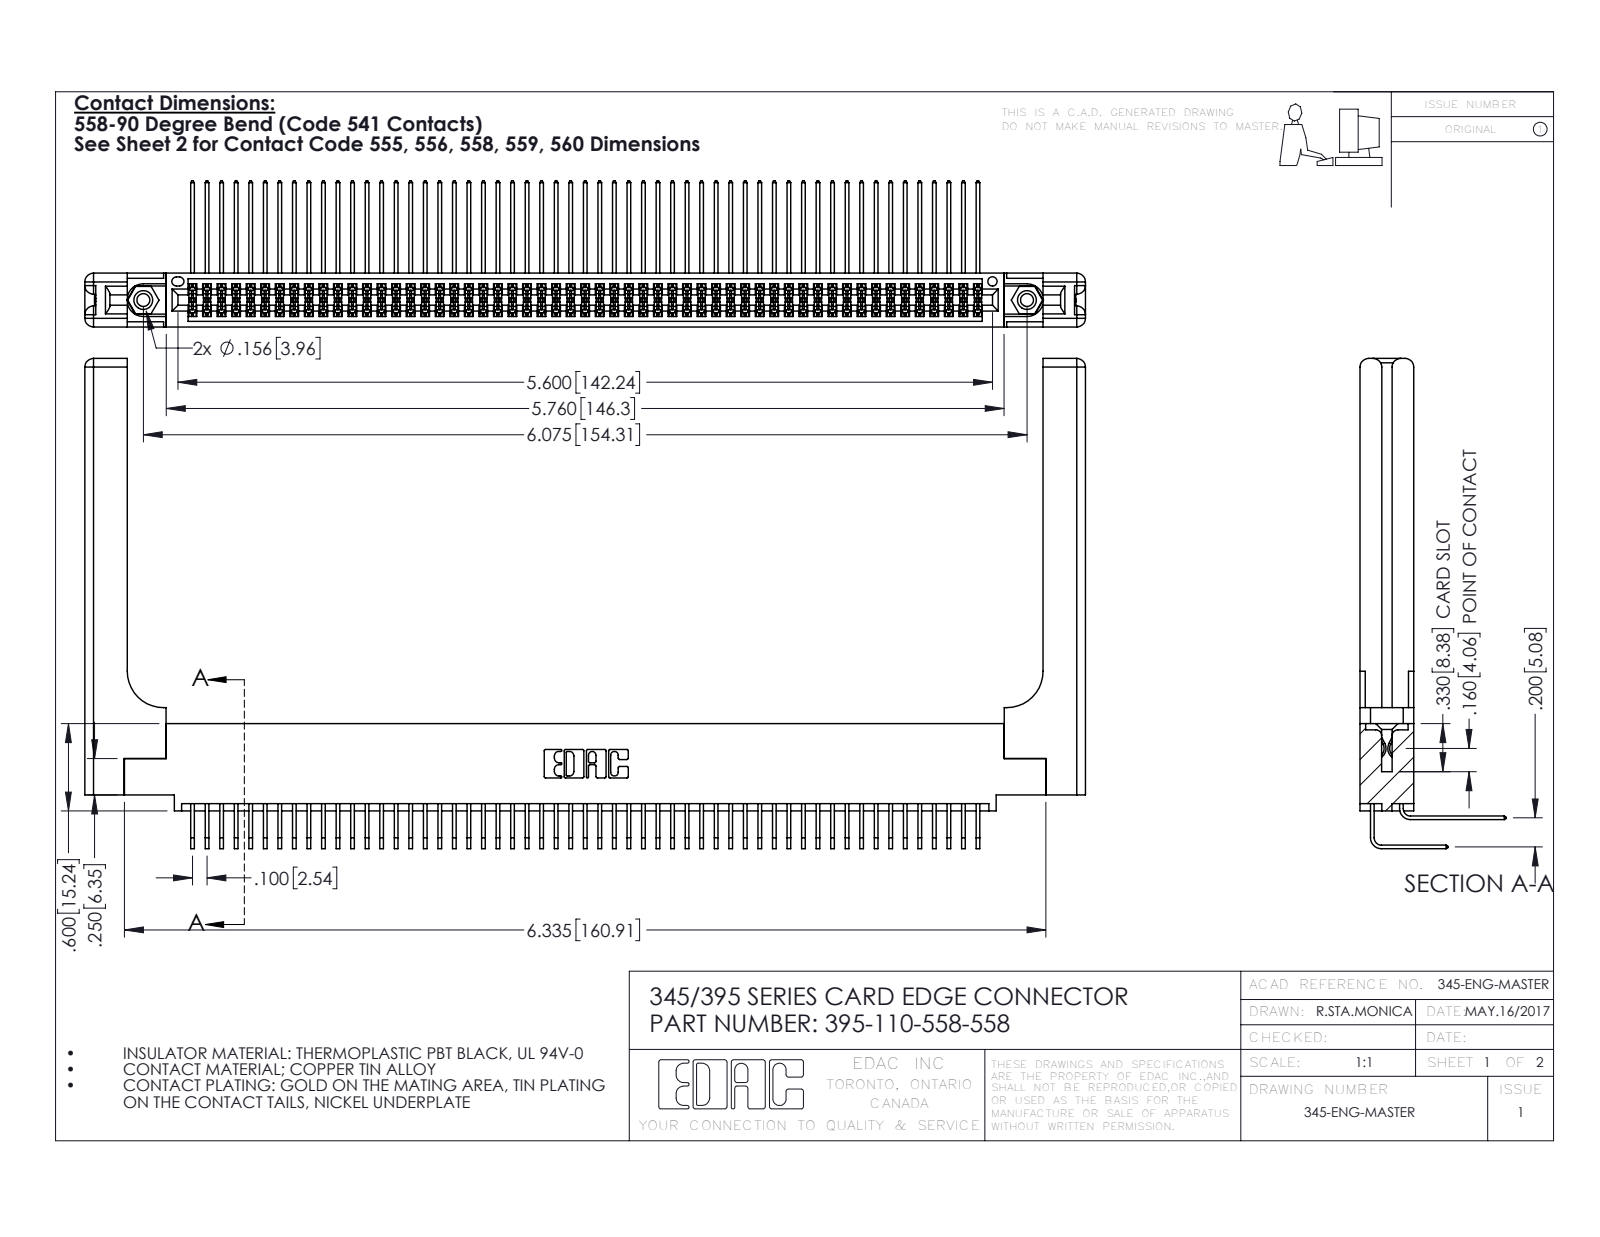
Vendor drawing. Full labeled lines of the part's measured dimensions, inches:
Part name (STEP PRODUCT): 345 Part_0.110 Offset - 0.156 Dia-TH; 345-250-001_345-250-001-102; 345-292-001_558 Tail - 2; 345-220-058_345-220-058 (+2 more)
STEP written by: SolidWorks 2016 (CONFIG_CONTROL_DESIGN)
Units: inches
Bodies: 115 solids, 6106 faces (4082 planar, 1964 cylindrical, 60 other)
Overall size (bounding box): 6.879 × 3.369 × 1.005
Volume: 1.595 in³ · Surface area: 53.45 in²
Round holes (diameter × count): ⌀0.089 ×2, ⌀0.125 ×2, ⌀0.156 ×2, ⌀0.064 ×1
Round bosses / shafts (diameter × count): ⌀0.155 ×2
Partial cylindrical surfaces — rounded edges, fillets, slot ends (radius × count): R0.006 ×165, R0.01 ×22, R0.06 ×16, R0.007 ×6, R0.031 ×6, R0.026 ×3, R0.014 ×2, R0.019 ×2
Main face-to-face distances: 0.072, 0.298, 0.37, 0.2, 0.098, 0.272, 0.025, 0.225, 0.148, 0.15
Hole centre spacings: 0.27, 5.839, 6.075
